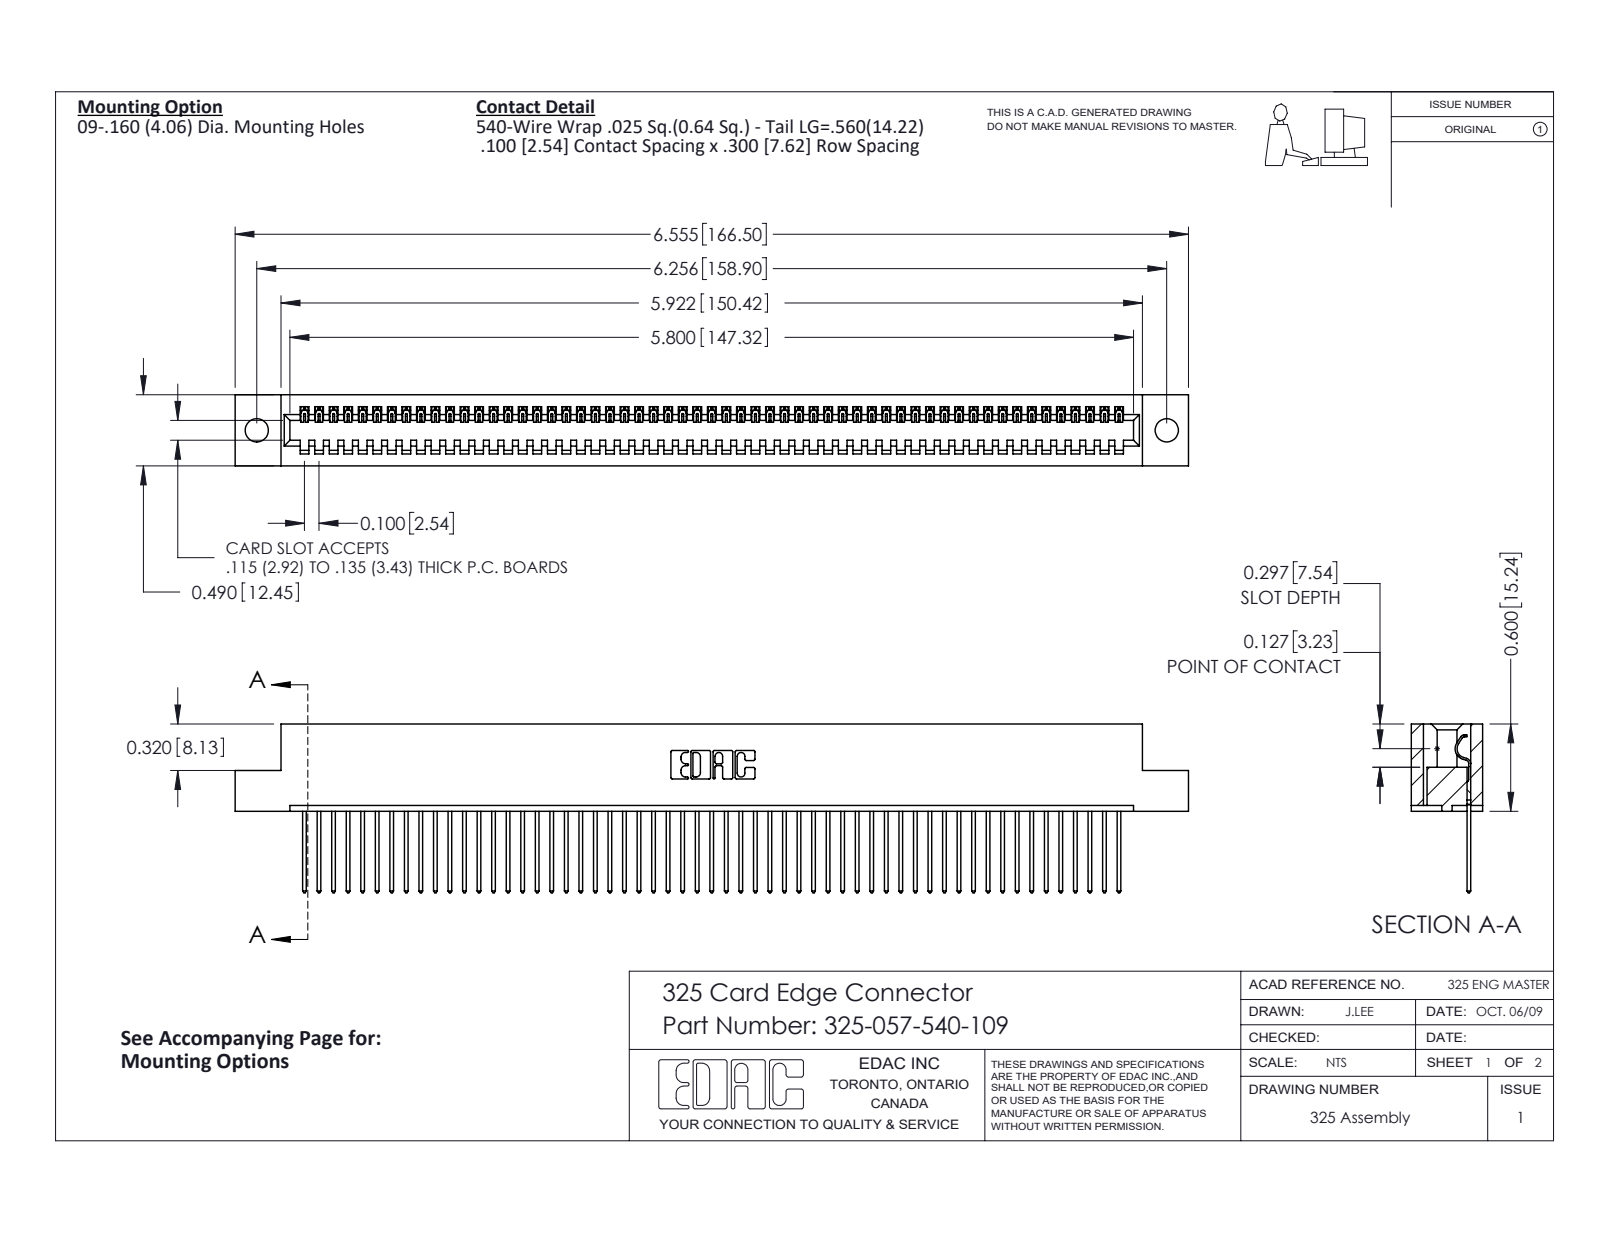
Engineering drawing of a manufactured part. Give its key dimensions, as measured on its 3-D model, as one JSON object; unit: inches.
{"part_name": "325-057-540-109; 325-292-001_325-293-140; 325 Part_.160 TH", "step_written_by": "SolidWorks 2016 (CONFIG_CONTROL_DESIGN)", "units": "inches", "bodies": {"solids": 58, "faces": 3420, "planar": 2464, "cylindrical": 956, "other": 0}, "overall_size": [6.555, 1.16, 0.49], "volume_in3": 1.288, "surface_area_in2": 36.85, "round_holes": [[0.16, 2]], "partial_cylinders_radius": [[0.006, 114], [0.01, 114], [0.01, 22], [0.007, 6], [0.031, 6], [0.026, 3], [0.014, 1], [0.022, 1]], "face_to_face_distances": [0.083, 0.407, 0.3, 0.49, 0.107, 0.383, 0.025, 0.325, 0.56, 0.263], "hole_center_spacings": [6.256]}
